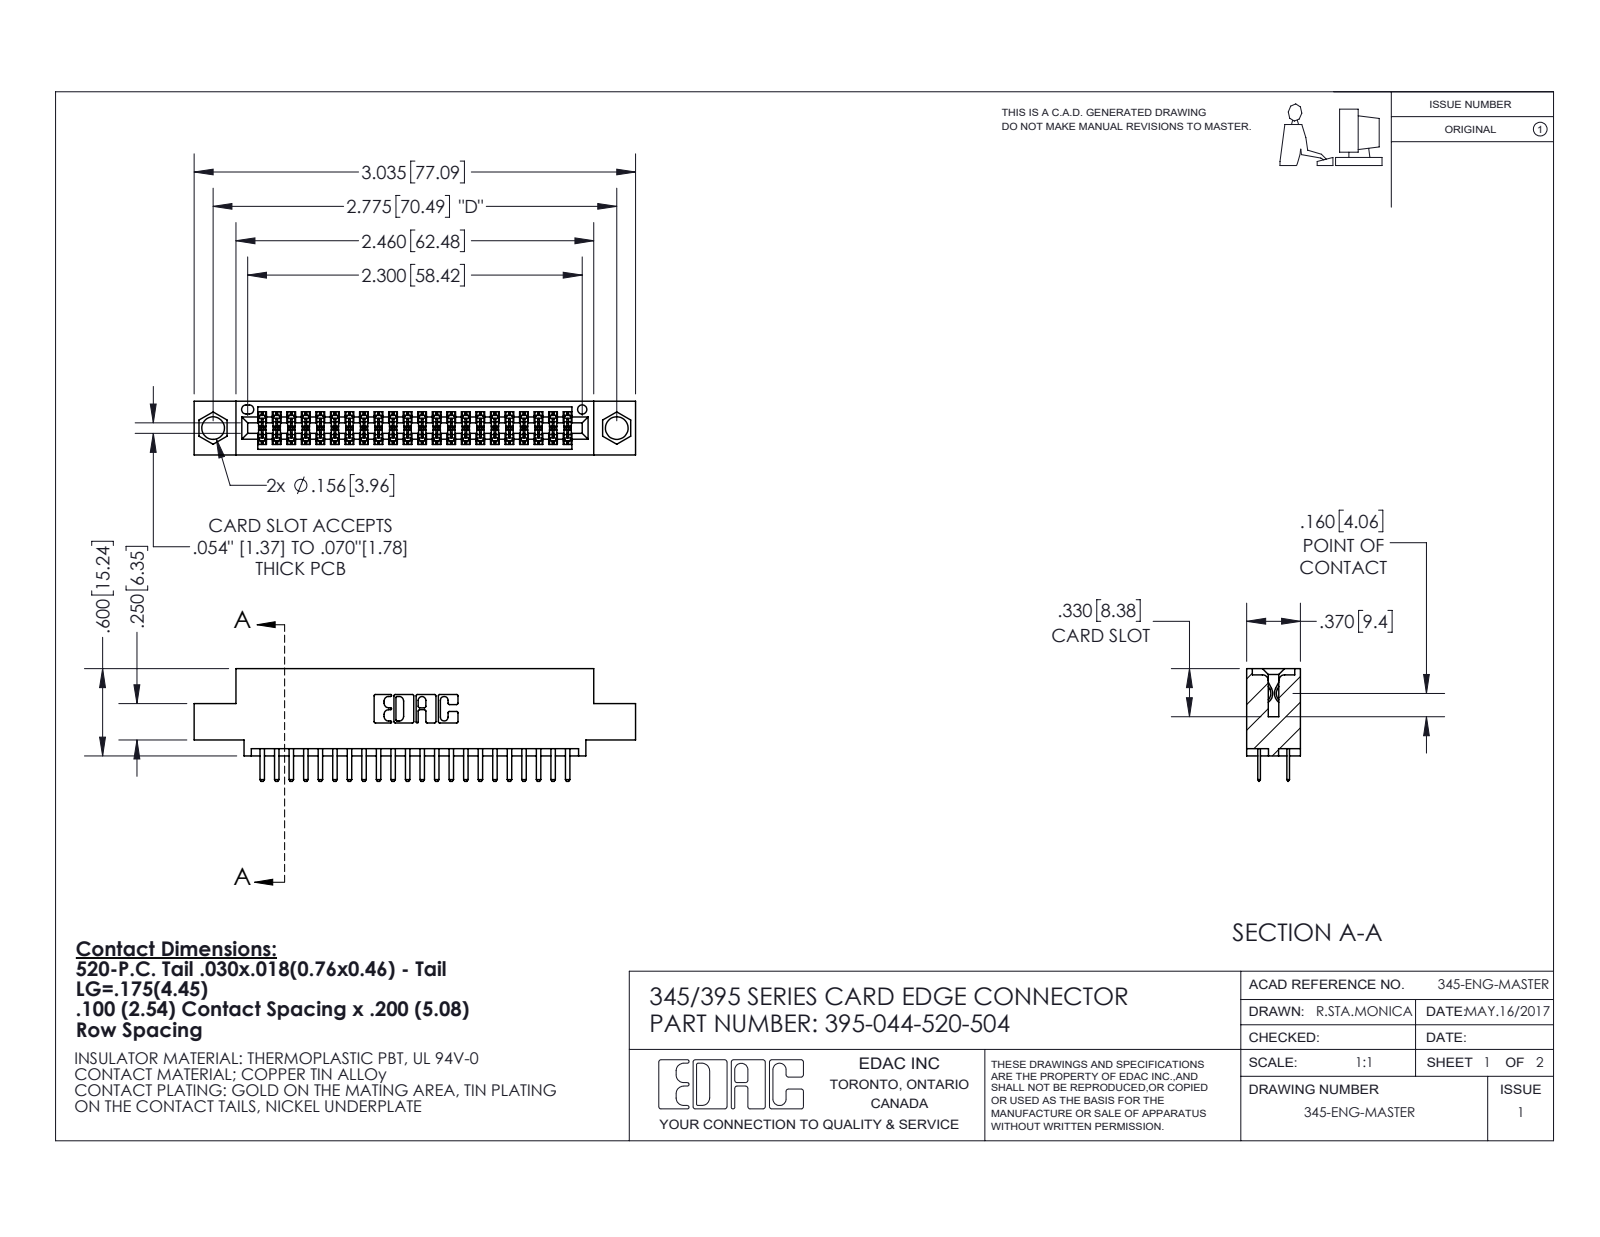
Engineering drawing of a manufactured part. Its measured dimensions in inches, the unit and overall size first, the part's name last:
Units: inches
Overall size (bounding box): 3.035 × 0.775 × 0.37
Round holes (diameter × count): ⌀0.156 ×2, ⌀0.064 ×1
Partial cylindrical surfaces — rounded edges, fillets, slot ends (radius × count): R0.006 ×66, R0.01 ×48, R0.01 ×22, R0.007 ×6, R0.031 ×6, R0.026 ×3, R0.014 ×2, R0.019 ×2
Main face-to-face distances: 0.298, 0.072, 0.2, 0.37, 0.098, 0.272, 0.025, 0.225, 0.022, 0.072
Hole centre spacings: 0.27, 2.541, 2.775
Volume: 0.434 in³ · Surface area: 15.53 in²
Bodies: 45 solids, 2520 faces (1638 planar, 882 cylindrical, 0 other)
Part name (STEP PRODUCT): 395-044-520-504; 345-292-001_345-293-120; 345 Part_0.110 Offset - 0.156 Dia-TI
STEP written by: SolidWorks 2020 (CONFIG_CONTROL_DESIGN)
